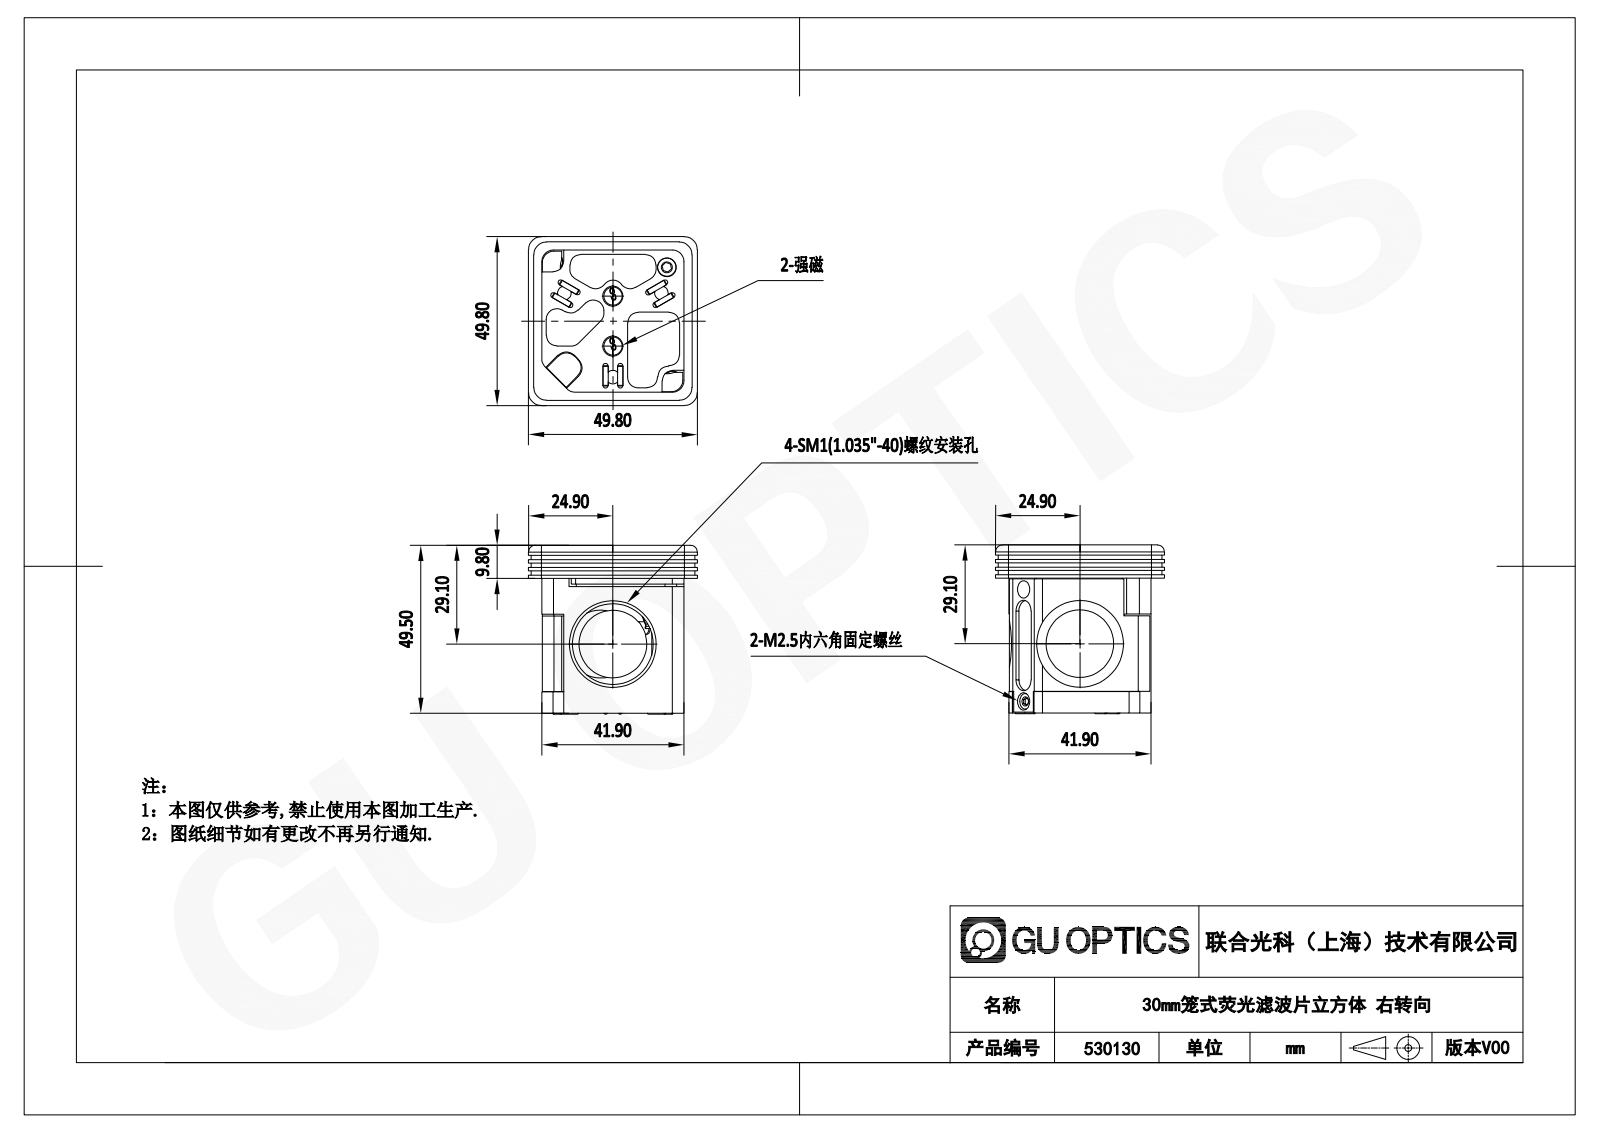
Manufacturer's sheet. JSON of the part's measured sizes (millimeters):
{"part_name": "530130", "step_written_by": "SolidWorks 2020 (CONFIG_CONTROL_DESIGN)", "units": "millimeters", "bodies": {"solids": 17, "faces": 654, "planar": 361, "cylindrical": 199, "other": 94}, "overall_size": [49.78, 49.78, 49.76], "volume_mm3": 42919, "surface_area_mm2": 31167, "round_holes": [[5.08, 4], [2.5, 3], [3.4, 3], [4, 3], [5.6, 3], [25.6, 3], [1.6, 2], [2.05, 2], [2.1, 2], [2.9, 2], [6, 2], [20, 2]], "round_bosses_or_shafts": [[1.5, 6], [5.5, 3], [3, 3], [4.6, 1], [2.5, 1], [2, 1]], "partial_cylinders_radius": [[3.17, 29], [0.79, 12], [3.43, 12], [3.81, 8], [6.35, 5], [1.59, 4], [1.59, 4], [1.78, 4]], "face_to_face_distances": [1.27, 48.26, 41.91, 0.76, 2.54, 40.16, 6.35, 2.61, 8.1, 49.53], "hole_center_spacings": [32.99, 36.4, 13.99, 14.33, 21.18, 28.59, 30.45, 33.44]}
